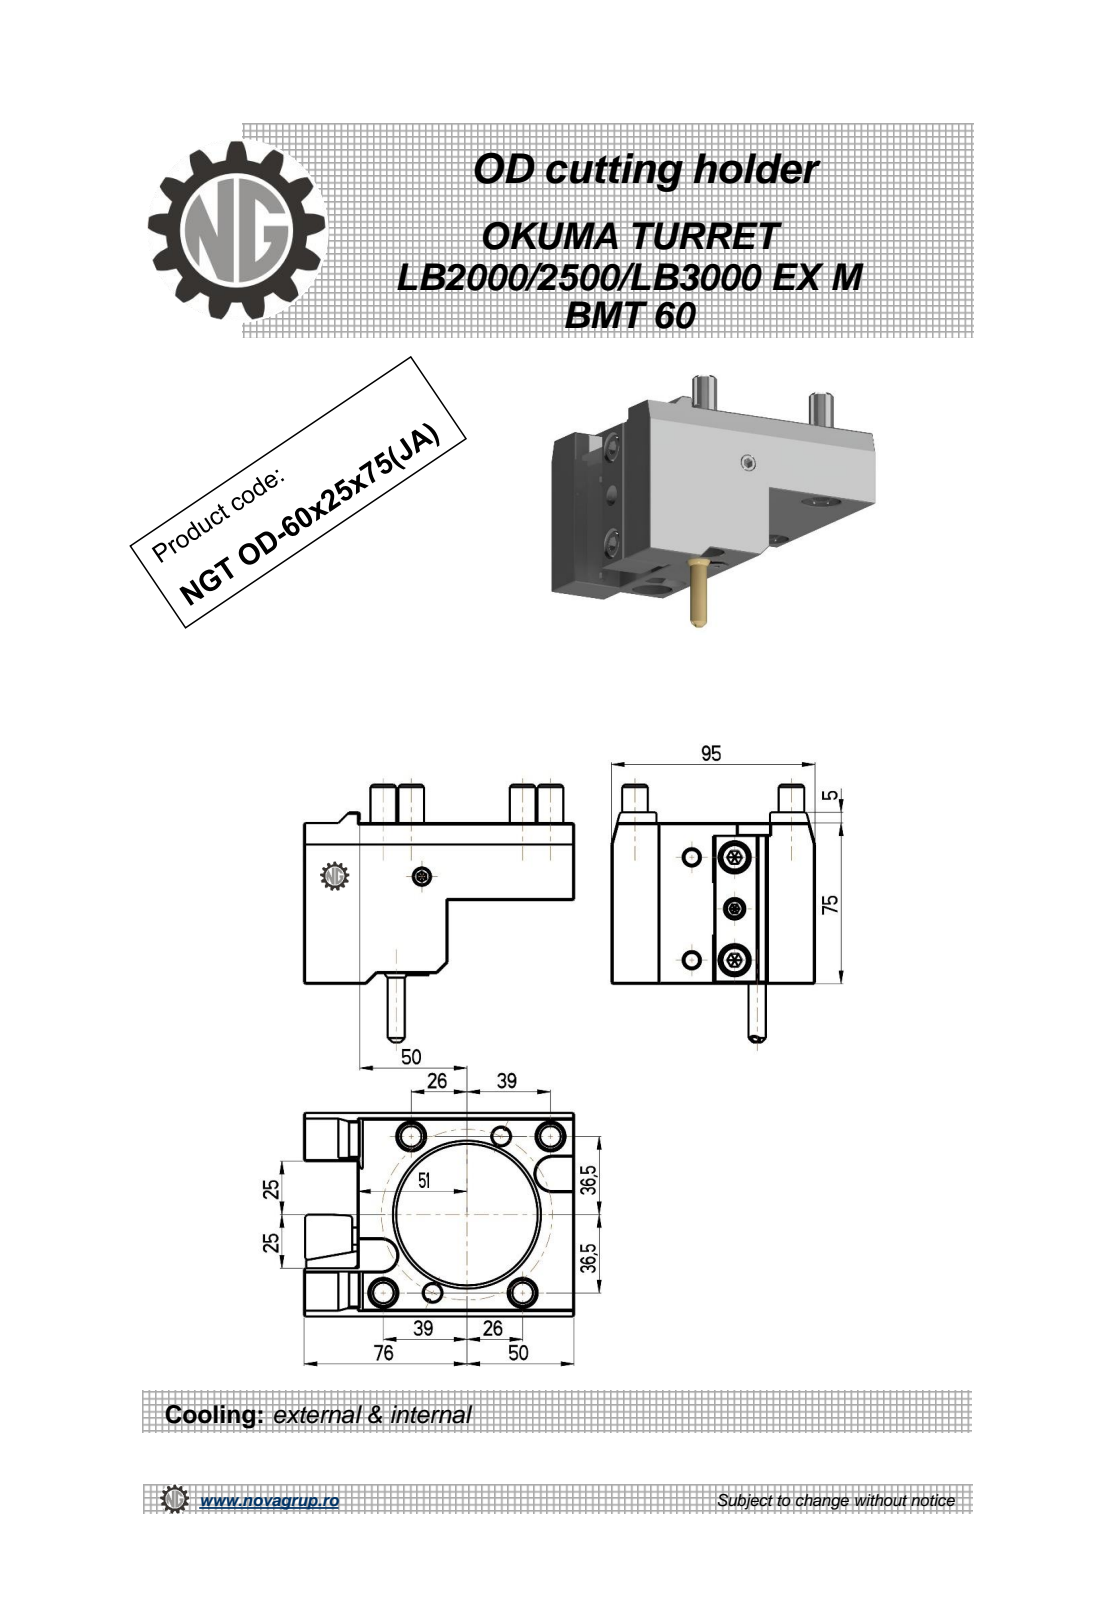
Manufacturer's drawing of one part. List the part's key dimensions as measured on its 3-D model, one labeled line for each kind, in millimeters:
Part name (STEP PRODUCT): NGT_OD_60_25_75_JA
STEP written by: PRO/ENGINEER BY PARAMETRIC TECHNOLOGY CORPORATION, 2010280 (CONFIG_CONTROL_DESIGN)
Units: millimetres
Bodies: 1 solid, 208 faces (137 planar, 43 cylindrical, 28 other)
Overall size (bounding box): 126 × 120.34 × 95
Volume: 605 838 mm³ · Surface area: 63 648 mm²
Round holes (diameter × count): ⌀8.2 ×2, ⌀3 ×1, ⌀5 ×1, ⌀69 ×1
Round bosses / shafts (diameter × count): ⌀12 ×4, ⌀8 ×4, ⌀61 ×1, ⌀11.2 ×1
Partial cylindrical surfaces — rounded edges, fillets, slot ends (radius × count): R0.22 ×6, R0.4 ×2, R4 ×2, R1 ×1, R7.5 ×1, R8 ×1
Main face-to-face distances: 36, 95, 25, 126, 101, 59, 42, 67, 70, 34
Hole centre spacings: 39.85, 23.35, 38.85, 75.17, 79.71
